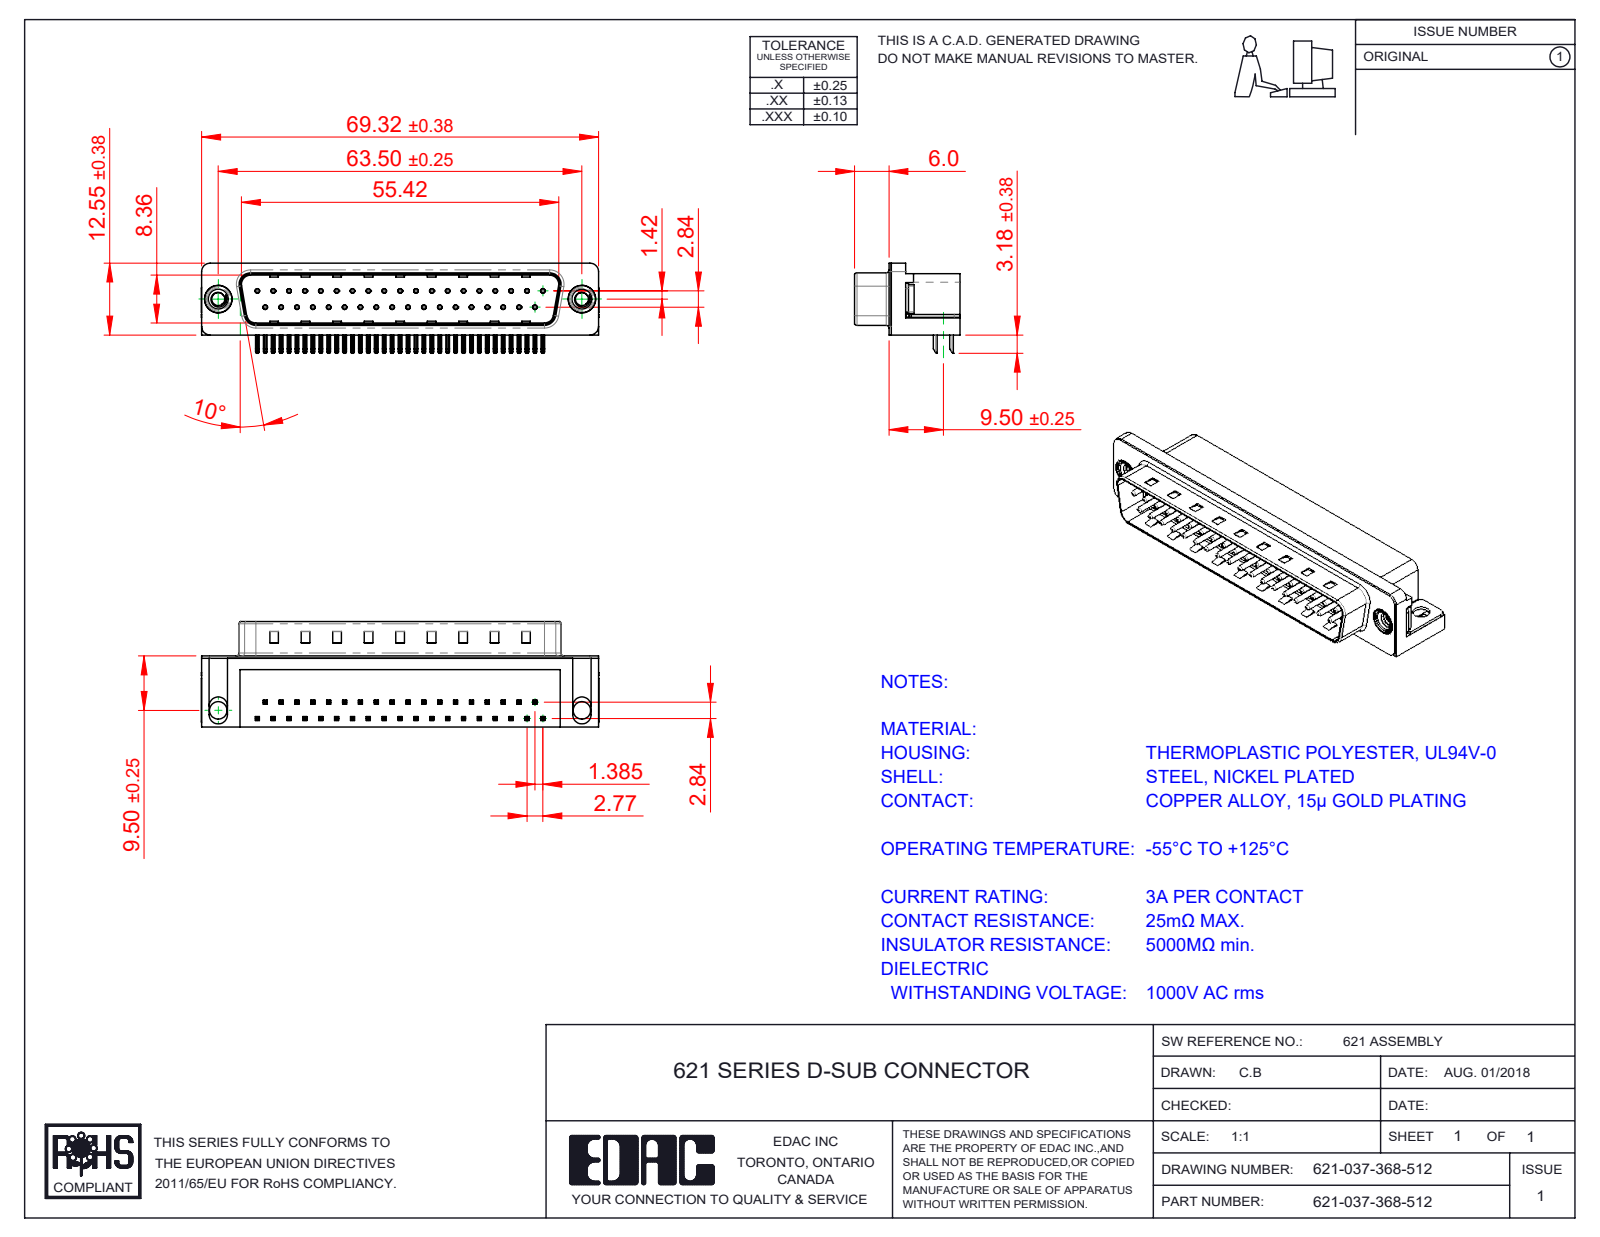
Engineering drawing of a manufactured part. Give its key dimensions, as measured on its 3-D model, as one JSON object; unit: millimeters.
{"part_name": "621 4-40 Threaded Rivet; 621-037-368-512; 621 Thru Hole Board Mount; 621 Housing_37 Socket (+3 more)", "step_written_by": "SolidWorks 2016 (CONFIG_CONTROL_DESIGN)", "units": "millimeters", "bodies": {"solids": 43, "faces": 3197, "planar": 2011, "cylindrical": 915, "other": 271}, "overall_size": [69.4, 18.4, 15.73], "volume_mm3": 8620, "surface_area_mm2": 10081, "round_holes": [[0.35, 37], [0.8, 37], [2.26, 2], [3.05, 2], [4, 2], [4.8, 2], [5, 2]], "round_bosses_or_shafts": [[0.75, 37], [4.9, 2], [4.75, 2], [3.9, 2]], "partial_cylinders_radius": [[0.25, 156], [0.12, 74], [1, 16], [0.5, 9], [1.6, 8], [1.5, 7], [0.9, 4], [2, 4]], "face_to_face_distances": [0.4, 12, 10.35, 8.76, 2.1, 1.7, 10.46, 10.86, 9, 12.4], "hole_center_spacings": [3.16, 2.77, 5.54, 8.31, 11.08, 13.85, 19.39, 22.16]}
